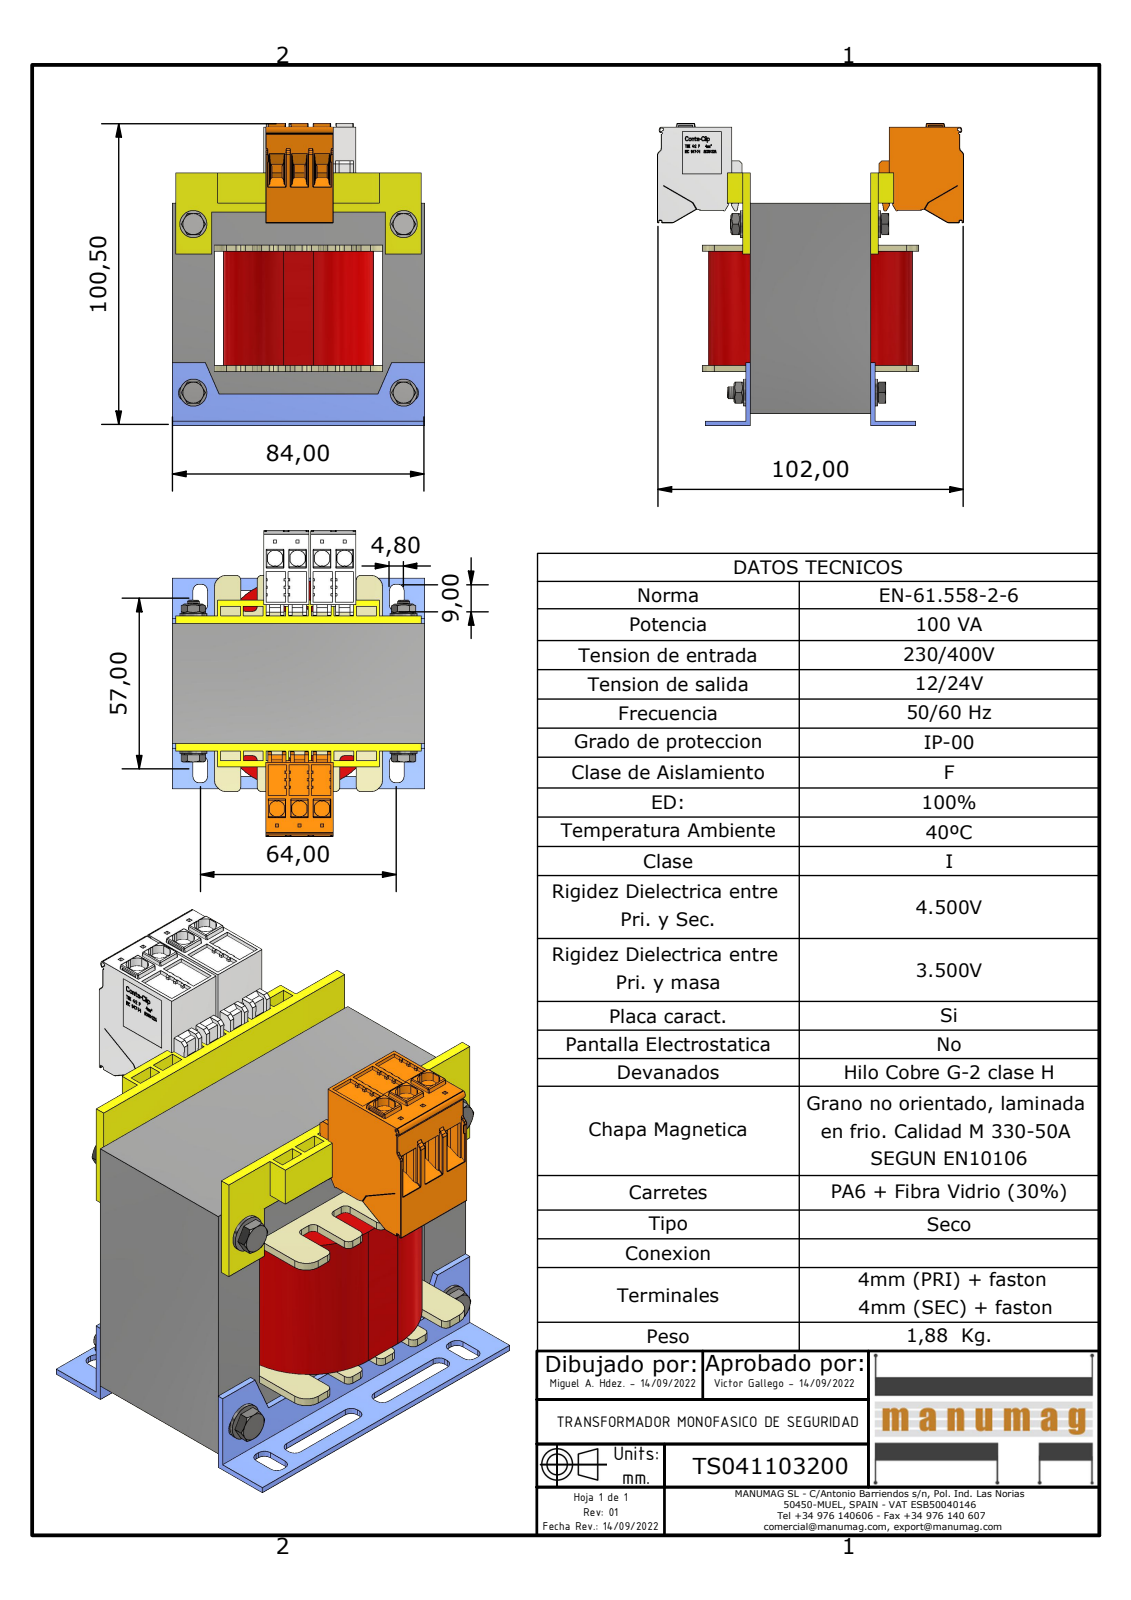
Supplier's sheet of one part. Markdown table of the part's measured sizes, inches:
| quantity | value |
| --- | --- |
| part name | TS041103200; EI84 x 70 - 40 (RC28); EI 84 X 70 - 40; EI84 (+6 more) |
| STEP written by | Autodesk Inventor 2023 (AUTOMOTIVE_DESIGN) |
| units | inches |
| bodies | 25 solids, 5812 faces (4692 planar, 757 cylindrical, 363 other) |
| overall size | 4.012 × 3.957 × 3.307 |
| volume | 19.29 in³ |
| surface area | 155.2 in² |
| round holes (diameter × count) | 0.128 × 4, 0.169 × 4, 0.177 × 4, 0.157 × 2 |
| round bosses / shafts (diameter × count) | 0.354 × 4, 0.232 × 4, 0.143 × 4, 0.157 × 2 |
| partial cylindrical surfaces (radius × count) | 0.006 × 271, 0.008 × 86, 0.079 × 40, 0.059 × 32, 0.02 × 22, 0.012 × 12, 0.039 × 8, 0.106 × 7 |
| main face-to-face distances | 0.551, 2.205, 1.575, 1.102, 1.654, 2.756, 0.098, 0.059, 3.307, 0.079 |
| hole center spacings | 2.205, 2.756, 3.529 |
